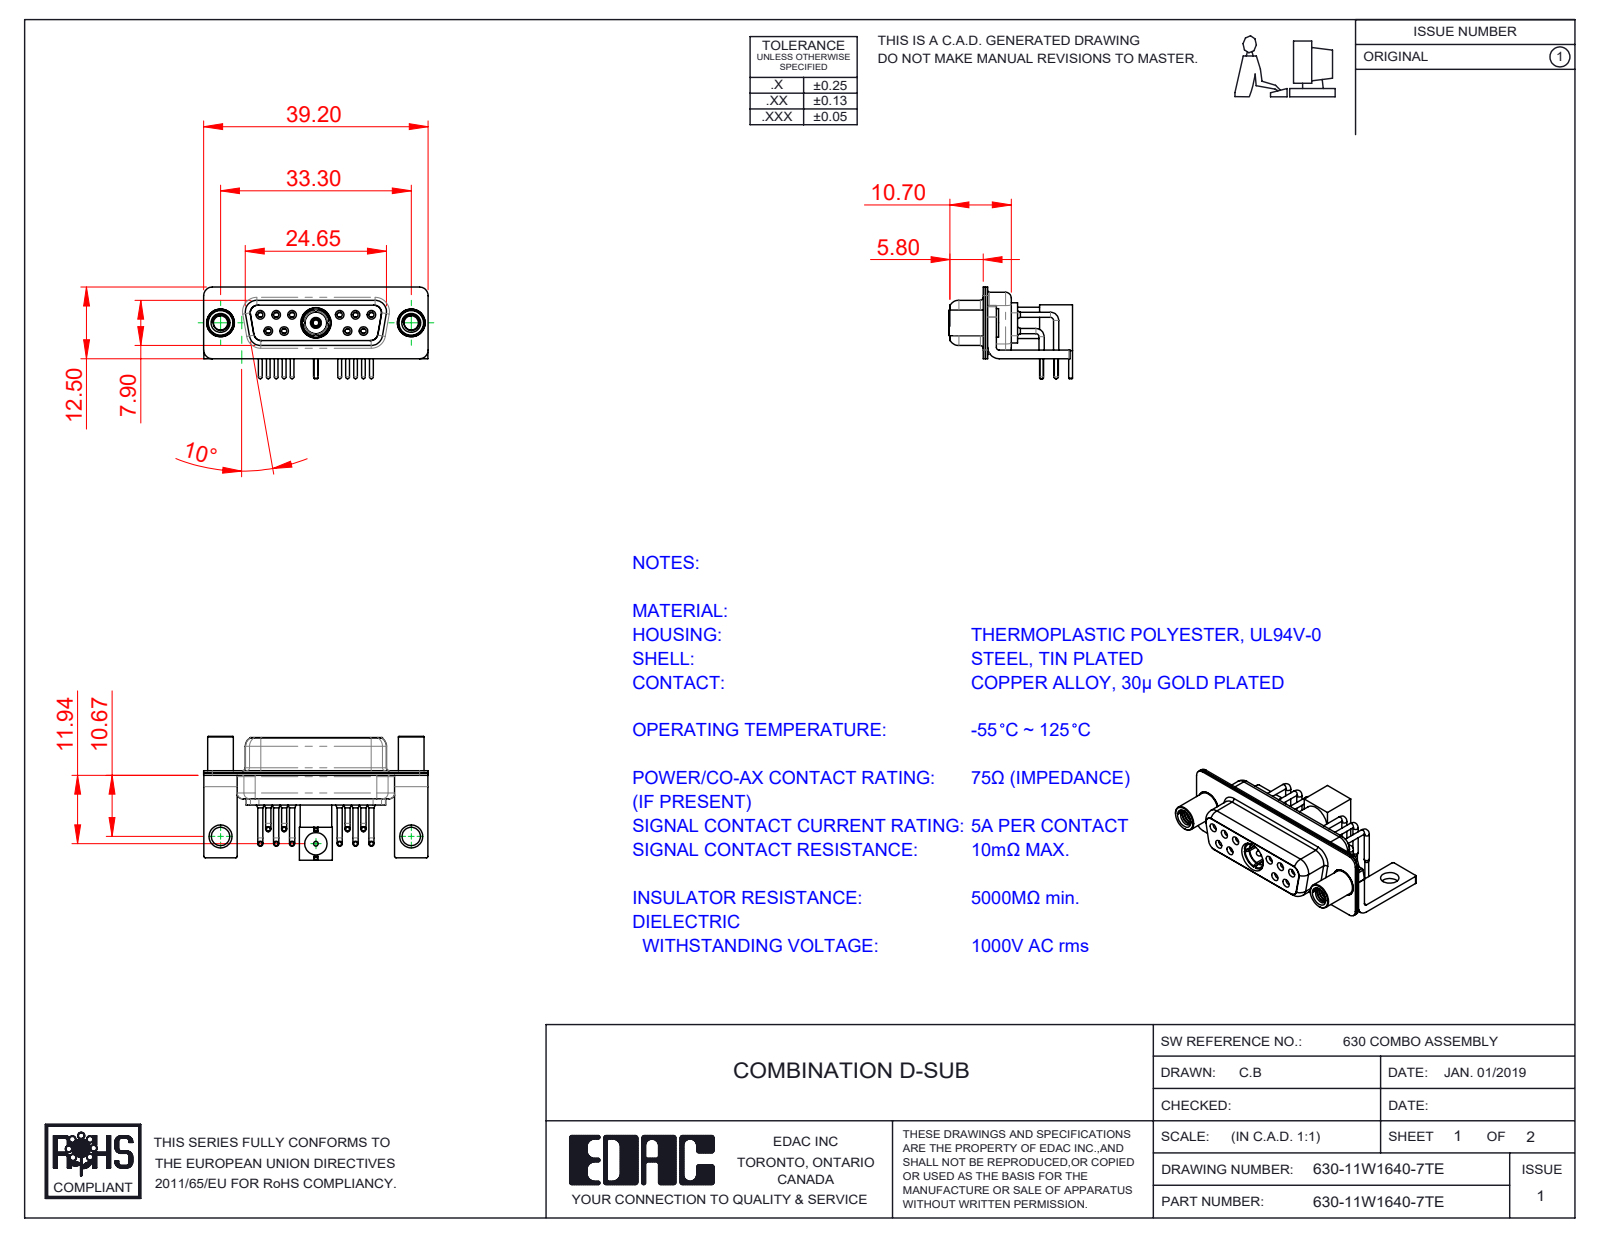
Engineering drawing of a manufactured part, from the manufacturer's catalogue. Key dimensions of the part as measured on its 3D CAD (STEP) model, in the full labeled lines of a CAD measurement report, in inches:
Part name (STEP PRODUCT): Pin_RA; RA Back Shell; 630Combo Contact Row 2; Insulator RA Pin (+8 more)
STEP written by: SolidWorks 2020 (CONFIG_CONTROL_DESIGN)
Units: inches
Bodies: 23 solids, 1075 faces (306 planar, 504 cylindrical, 265 other)
Overall size (bounding box): 1.543 × 0.851 × 0.63
Volume: 0.195 in³ · Surface area: 12.12 in²
Round holes (diameter × count): ⌀0.043 ×11, ⌀0.059 ×11, ⌀0.035 ×10, ⌀0.079 ×10, ⌀0.067 ×6, ⌀0.063 ×4, ⌀0.191 ×3, ⌀0.098 ×2, ⌀0.126 ×2, ⌀0.157 ×2, ⌀0.159 ×2, ⌀0.031 ×1
Round bosses / shafts (diameter × count): ⌀0.035 ×10, ⌀0.026 ×10, ⌀0.063 ×6, ⌀0.197 ×3, ⌀0.195 ×2, ⌀0.189 ×2, ⌀0.177 ×2, ⌀0.217 ×1
Partial cylindrical surfaces — rounded edges, fillets, slot ends (radius × count): R0.01 ×16, R0.059 ×16, R0.079 ×13, R0.053 ×12, R0.063 ×8, R0.02 ×5, R0.024 ×4, R0.026 ×4
Main face-to-face distances: 0.016, 0.031, 0.055, 0.018, 0.071, 0.333, 0.35, 0.059, 0.244, 0.091
Hole centre spacings: 0.124, 0.109, 0.545, 0.436, 0.654, 0.198, 0.198, 0.218
